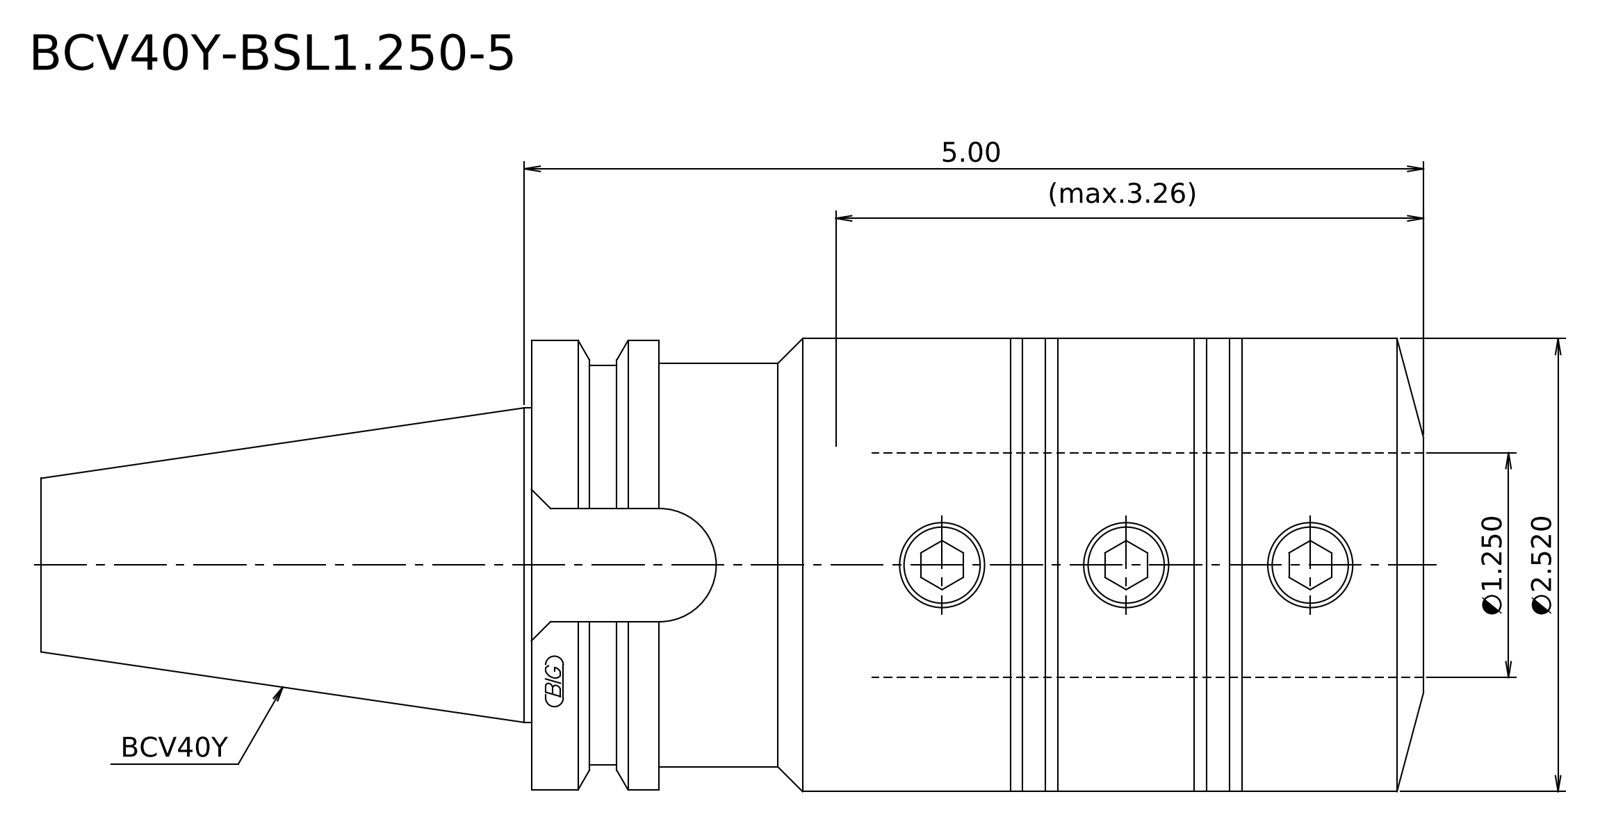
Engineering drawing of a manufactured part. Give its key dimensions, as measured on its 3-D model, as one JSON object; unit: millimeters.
{"step_written_by": "Kubotek KeyCreator 2011 V10.0.2 (22737) (automotive_design)", "units": "millimeters", "bodies": {"solids": 1, "faces": 17, "planar": 6, "cylindrical": 6, "other": 5}, "overall_size": [195.25, 64, 64], "volume_mm3": 451264, "surface_area_mm2": 38814, "round_bosses_or_shafts": [[64, 1], [63.5, 1], [57, 1], [56.36, 1], [44.45, 1]], "face_to_face_distances": [126, 107.95, 18.05, 195.25, 87.3, 69.25, 117.8, 9.85, 8.2, 77.45]}
